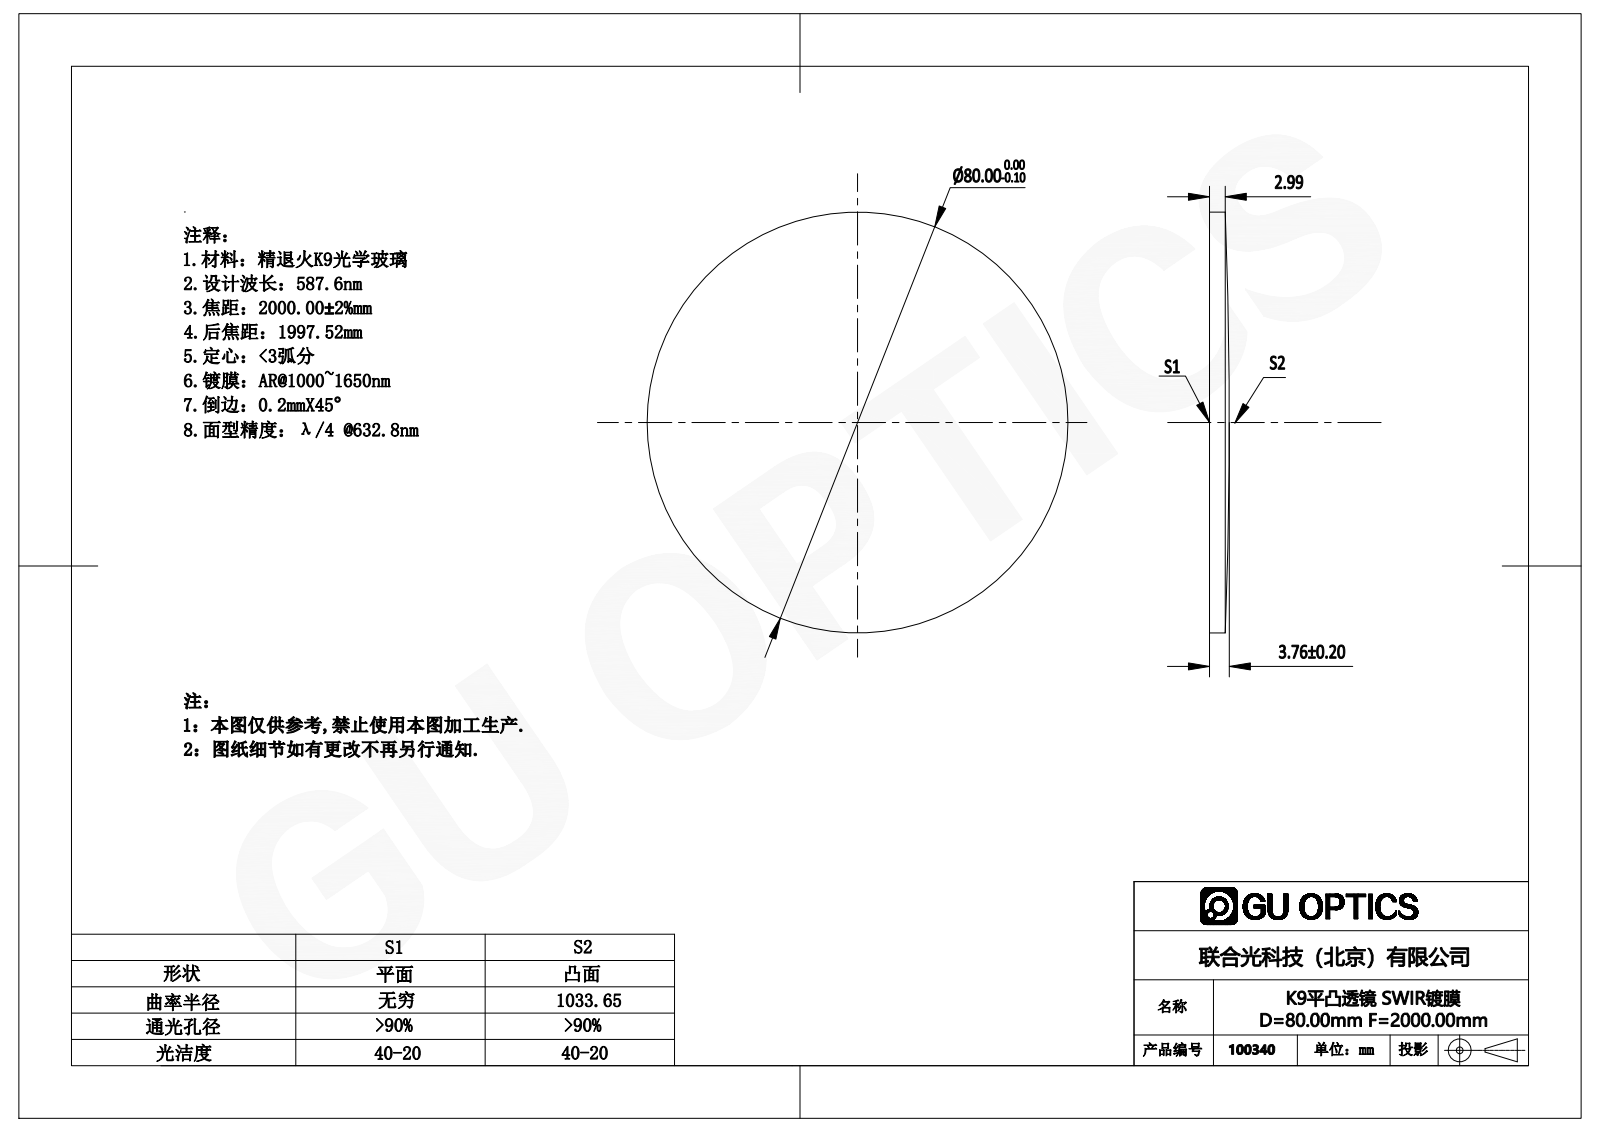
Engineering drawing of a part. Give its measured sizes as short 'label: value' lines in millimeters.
name: 100168
written by: SolidWorks 2016 (AUTOMOTIVE_DESIGN)
unit: mm
bodies: 1 solid, 5 faces (1 planar, 2 cylindrical, 2 other)
size: 80 × 80 × 3.76
volume: 16 965 mm³; area: 10 806 mm²
bosses: 1× ⌀80
